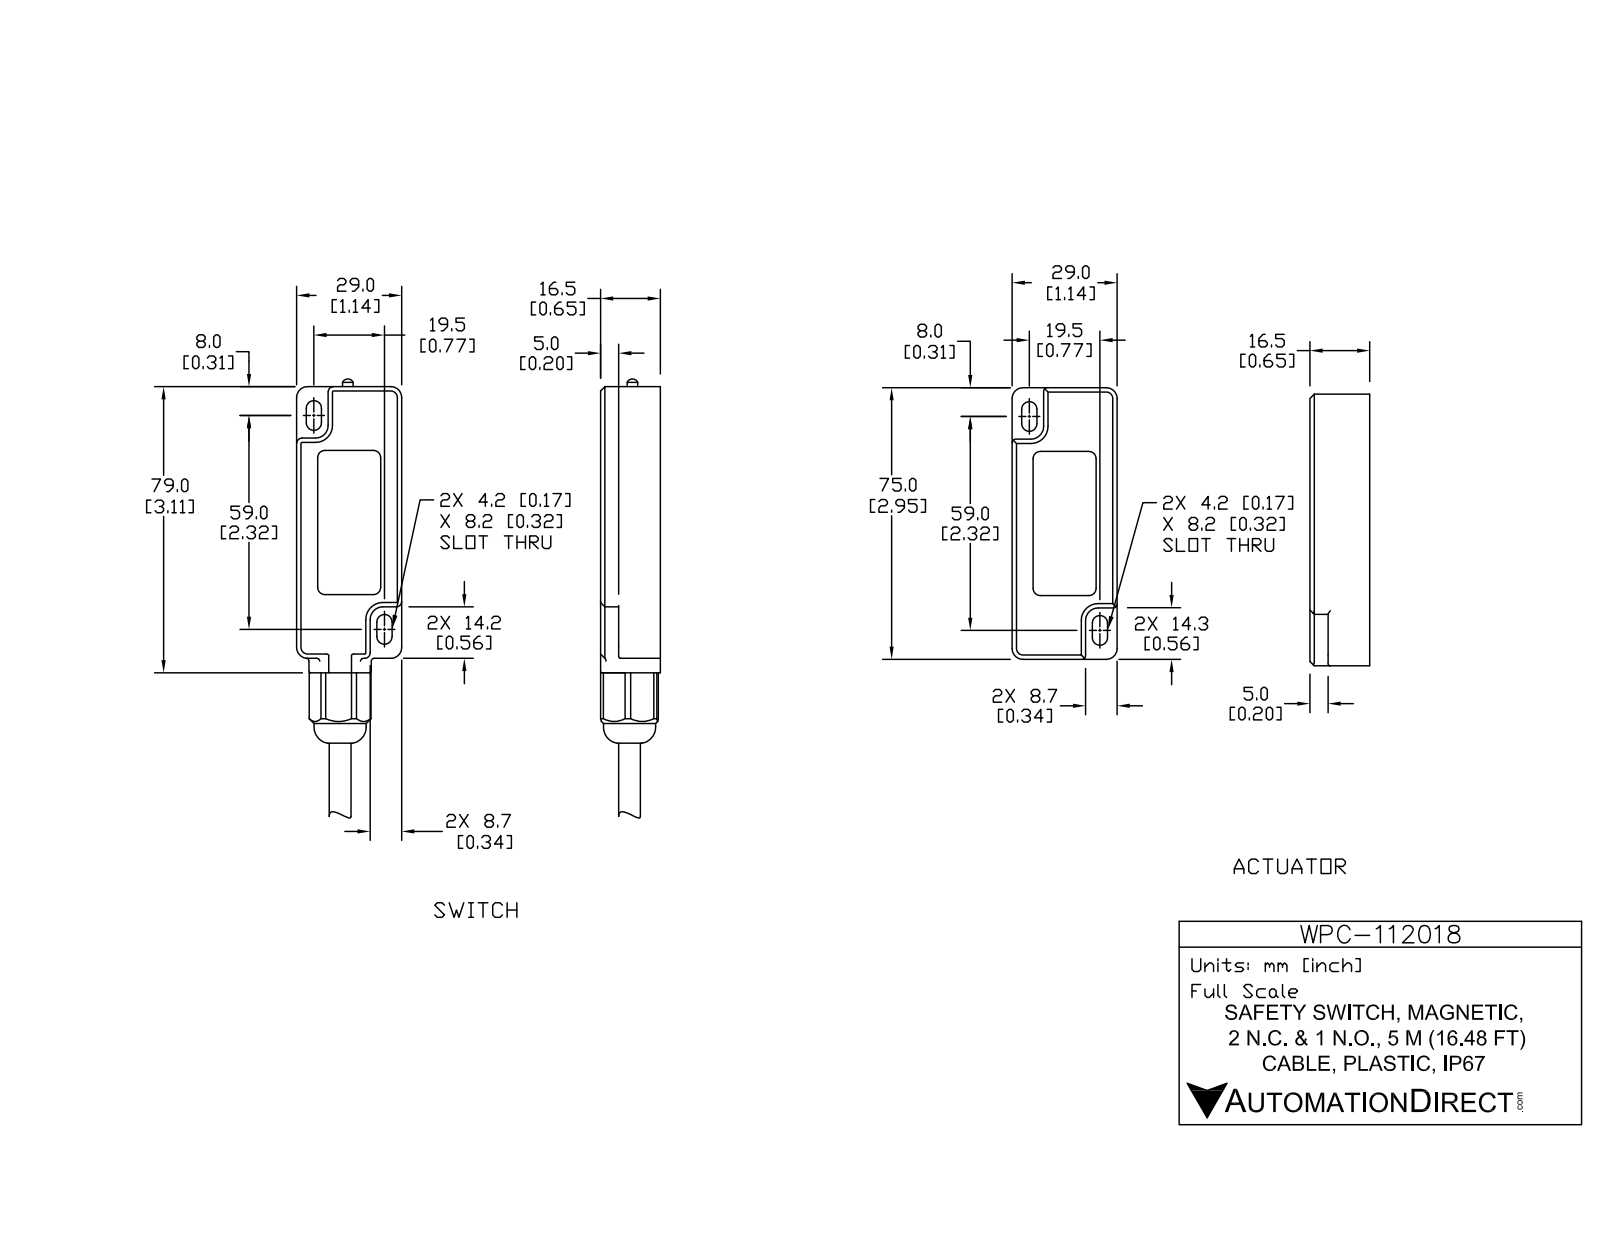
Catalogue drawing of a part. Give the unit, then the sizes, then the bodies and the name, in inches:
Units: inches
Overall size (bounding box): 9.241 × 2.323 × 0.65
Round holes (diameter × count): ⌀0.195 ×4, ⌀0.118 ×1, ⌀0.276 ×1, ⌀0.472 ×1
Round bosses / shafts (diameter × count): ⌀0.193 ×4, ⌀0.079 ×4, ⌀0.091 ×2, ⌀0.031 ×2, ⌀0.567 ×1, ⌀0.469 ×1, ⌀0.236 ×1, ⌀0.157 ×1
Partial cylindrical surfaces — rounded edges, fillets, slot ends (radius × count): R0.02 ×85, R0.039 ×20, R0.008 ×10, R0.047 ×8, R0.079 ×8, R0.083 ×8, R0.118 ×8, R0.024 ×4
Main face-to-face distances: 0.071, 0.575, 1.181, 1.071, 0.646, 0.067, 0.571, 0.075, 0.504, 0.579
Hole centre spacings: 2.047, 0.276, 0.9, 1.459, 2.344, 2.347
Volume: 2.25 in³ · Surface area: 58.13 in²
Bodies: 11 solids, 951 faces (420 planar, 244 cylindrical, 287 other)
Part name (STEP PRODUCT): WPC-112018; WPC-112018_1; WPC-112018_2
STEP written by: SolidWorks 2017 (AUTOMOTIVE_DESIGN)
